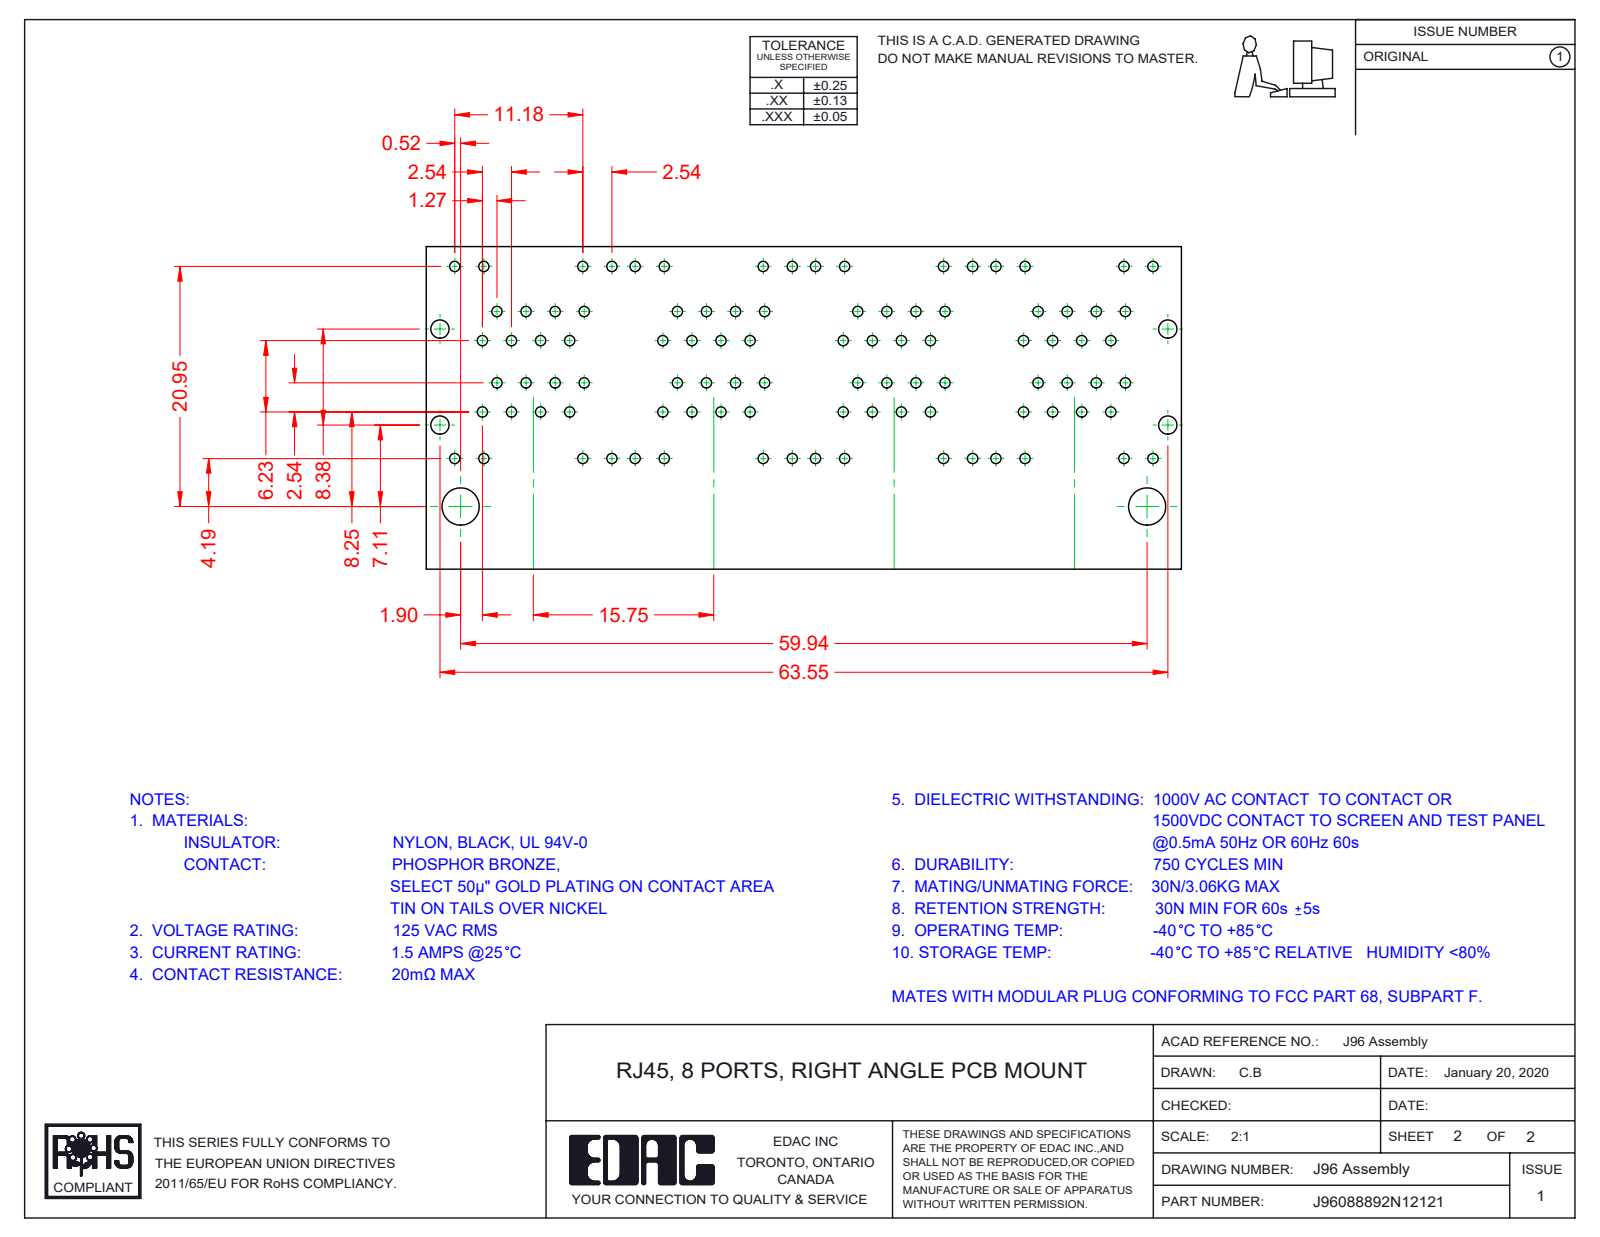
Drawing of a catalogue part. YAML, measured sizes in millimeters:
part_name: "96 LED LH Upper_1-Yellow; 96 Insulator Insert; J96088892N12121; 96 LED LH Lower_1-Yellow (+8 more)"
step_written_by: "SolidWorks 2016 (CONFIG_CONTROL_DESIGN)"
units: millimeters
bodies: {solids: 96, faces: 7642, planar: 6069, cylindrical: 1307, other: 266}
overall_size: [64.05, 29.58, 28.68]
volume: 24160
surface_area: 63658
round_holes:
  - {diameter: 1.7, count: 3}
round_bosses_or_shafts:
  - {diameter: 1.68, count: 3}
partial_cylinders:
  - {radius: 0.25, count: 124}
  - {radius: 0.35, count: 73}
  - {radius: 1, count: 72}
  - {radius: 0.5, count: 49}
  - {radius: 0.91, count: 32}
  - {radius: 0.2, count: 21}
  - {radius: 0.7, count: 11}
  - {radius: 0.22, count: 8}
face_to_face_distances: [15.75, 0.35, 9.95, 1.17, 1.6, 0.54, 9.98, 10.18, 12.67, 3.37]
hole_center_spacings: [15.75, 31.5]
